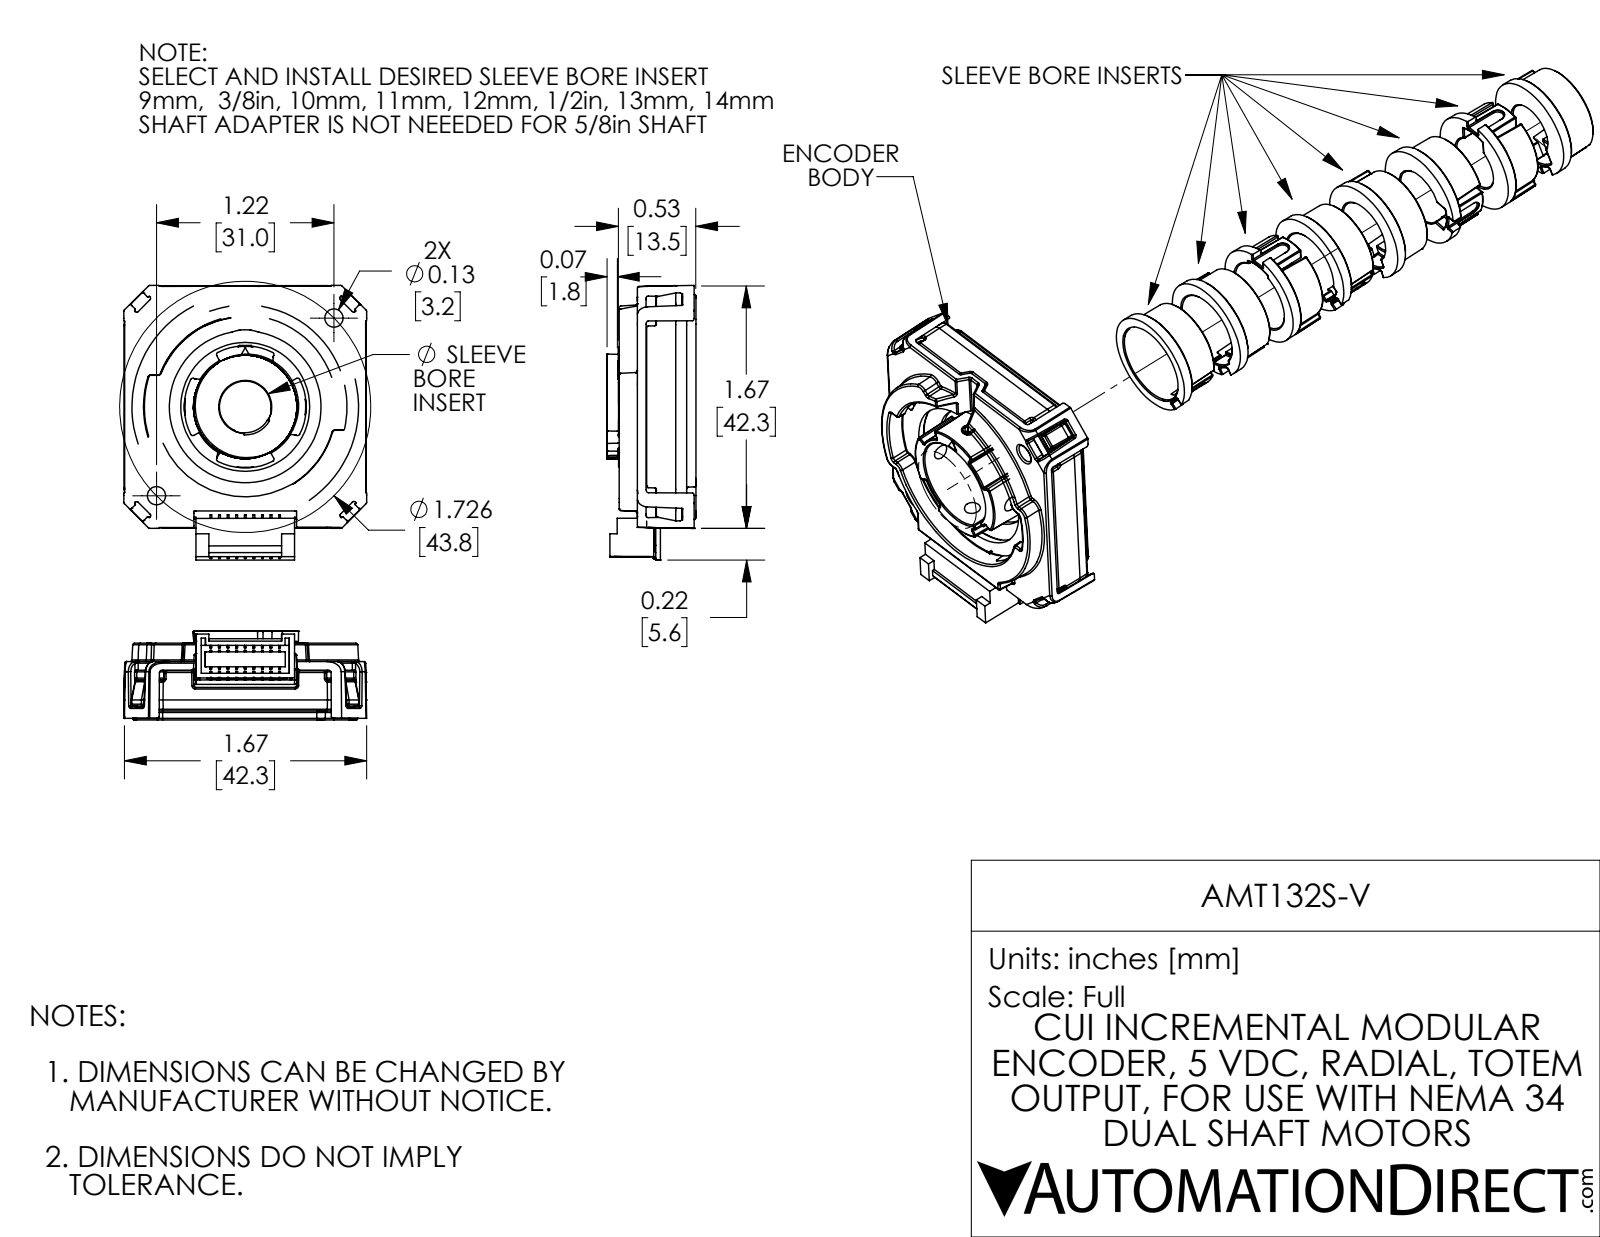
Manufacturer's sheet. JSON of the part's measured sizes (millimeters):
{"part_name": "AMT132S-V 1st r2", "step_written_by": "SolidWorks 2017 (AUTOMOTIVE_DESIGN)", "units": "millimeters", "bodies": {"solids": 25, "faces": 2769, "planar": 762, "cylindrical": 833, "other": 1174}, "overall_size": [143, 48, 42.4], "volume_mm3": 17800, "surface_area_mm2": 27230, "round_holes": [[0.8, 7], [0.6, 6], [2.8, 3], [2.5, 2], [2.6, 2], [3.3, 2], [2.1, 1], [21.5, 1], [22.5, 1], [35, 1]], "round_bosses_or_shafts": [[0.6, 4], [34, 1], [2.5, 1]], "partial_cylinders_radius": [[0.3, 304], [0.2, 172], [0.5, 46], [0.2, 28], [1.5, 24], [0.4, 13], [1.3, 8], [2, 8]], "face_to_face_distances": [1.5, 3.1, 1.6, 0.5, 0.8, 2.3, 1, 3.9, 4, 7.1], "hole_center_spacings": [31, 1.5, 1.5, 3, 21.9, 33.5, 39.6, 40.4]}
